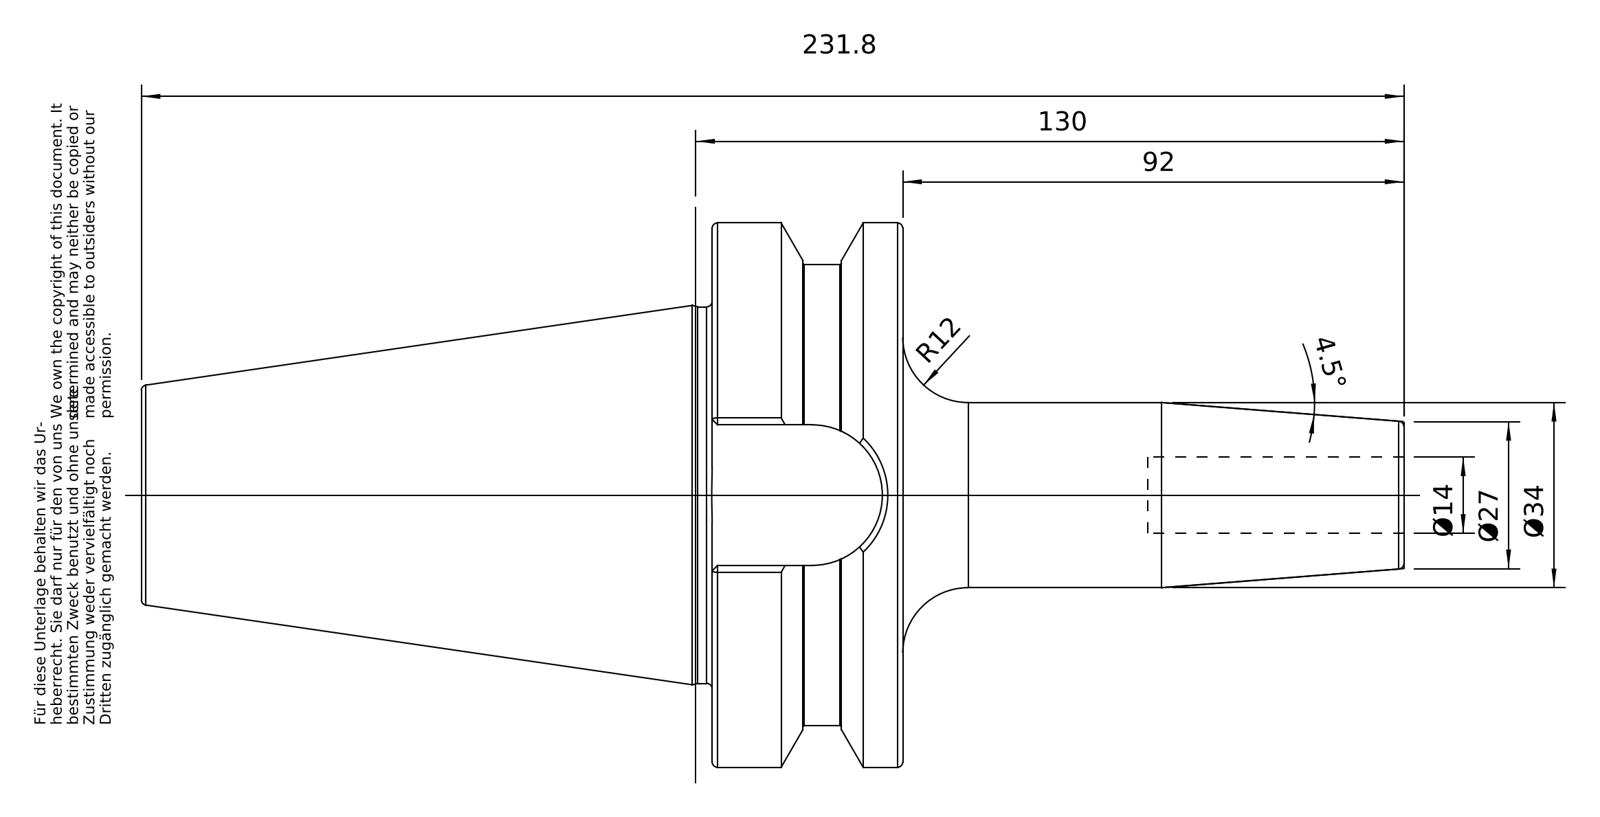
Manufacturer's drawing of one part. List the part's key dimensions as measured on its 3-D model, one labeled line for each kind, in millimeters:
Part name (STEP PRODUCT): 50-644-14
STEP written by: PRO/ENGINEER BY PARAMETRIC TECHNOLOGY CORPORATION, 2010430 (CONFIG_CONTROL_DESIGN)
Units: millimetres
Bodies: 1 solid, 96 faces (26 planar, 22 cylindrical, 48 other)
Overall size (bounding box): 231.8 × 99.97 × 99.97
Volume: 540 404 mm³ · Surface area: 62 414 mm²
Round holes (diameter × count): ⌀14 ×1, ⌀20.75 ×1, ⌀25.02 ×1, ⌀25.7 ×1
Round bosses / shafts (diameter × count): ⌀99.97 ×1, ⌀84.75 ×1, ⌀69.15 ×1, ⌀34 ×1, ⌀24.01 ×1
Partial cylindrical surfaces — rounded edges, fillets, slot ends (radius × count): R12.9 ×1
Main face-to-face distances: 35, 70.4, 104.8, 139.8, 25.8, 231.8, 127, 92, 184.8, 80
